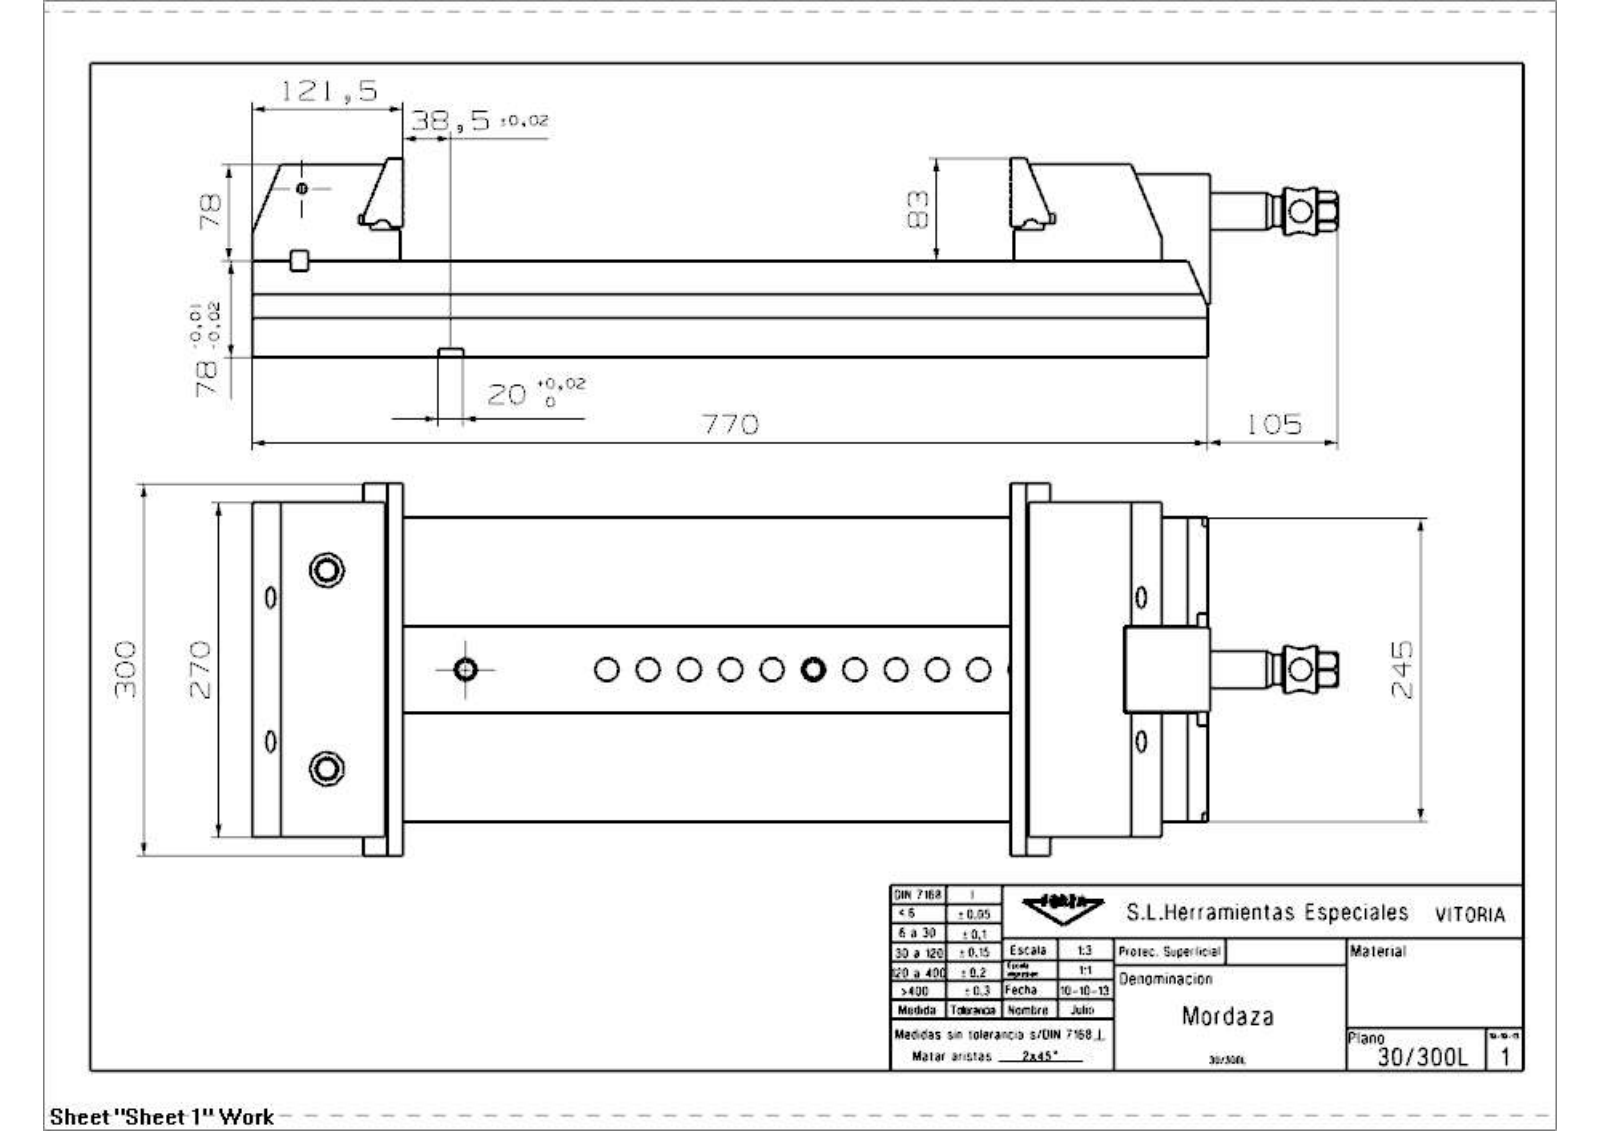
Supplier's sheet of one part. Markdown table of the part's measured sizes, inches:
| quantity | value |
| --- | --- |
| part name | 30_300L_Mordaza |
| STEP written by | SIEMENS PLM Software NX 7.5 (CONFIG_CONTROL_DESIGN) |
| units | inches |
| bodies | 11 solids, 403 faces (258 planar, 91 cylindrical, 54 other) |
| overall size | 34.445 × 11.811 × 6.331 |
| volume | 1 040 in³ |
| surface area | 1 829 in² |
| round holes (diameter × count) | 0.346 × 6, 0.748 × 6, 0.204 × 5, 0.709 × 5, 0.413 × 4, 0.417 × 4, 0.424 × 4, 0.453 × 4, 0.512 × 4, 0.63 × 4, 0.689 × 4, 0.551 × 2 |
| round bosses / shafts (diameter × count) | 1.496 × 1, 1.181 × 1, 0.945 × 1, 0.906 × 1, 0.709 × 1, 0.236 × 1 |
| partial cylindrical surfaces (radius × count) | 0.394 × 3, 0.276 × 2, 0.315 × 2, 0.472 × 1, 0.492 × 1, 0.62 × 1 |
| main face-to-face distances | 3.063, 0.071, 2.992, 1.535, 1.606, 1.457, 3.069, 9.646, 1.463, 2.998 |
| hole center spacings | 4.567, 6.221, 1.656, 0.014, 1.656, 1.656, 6.221, 7.874 |
